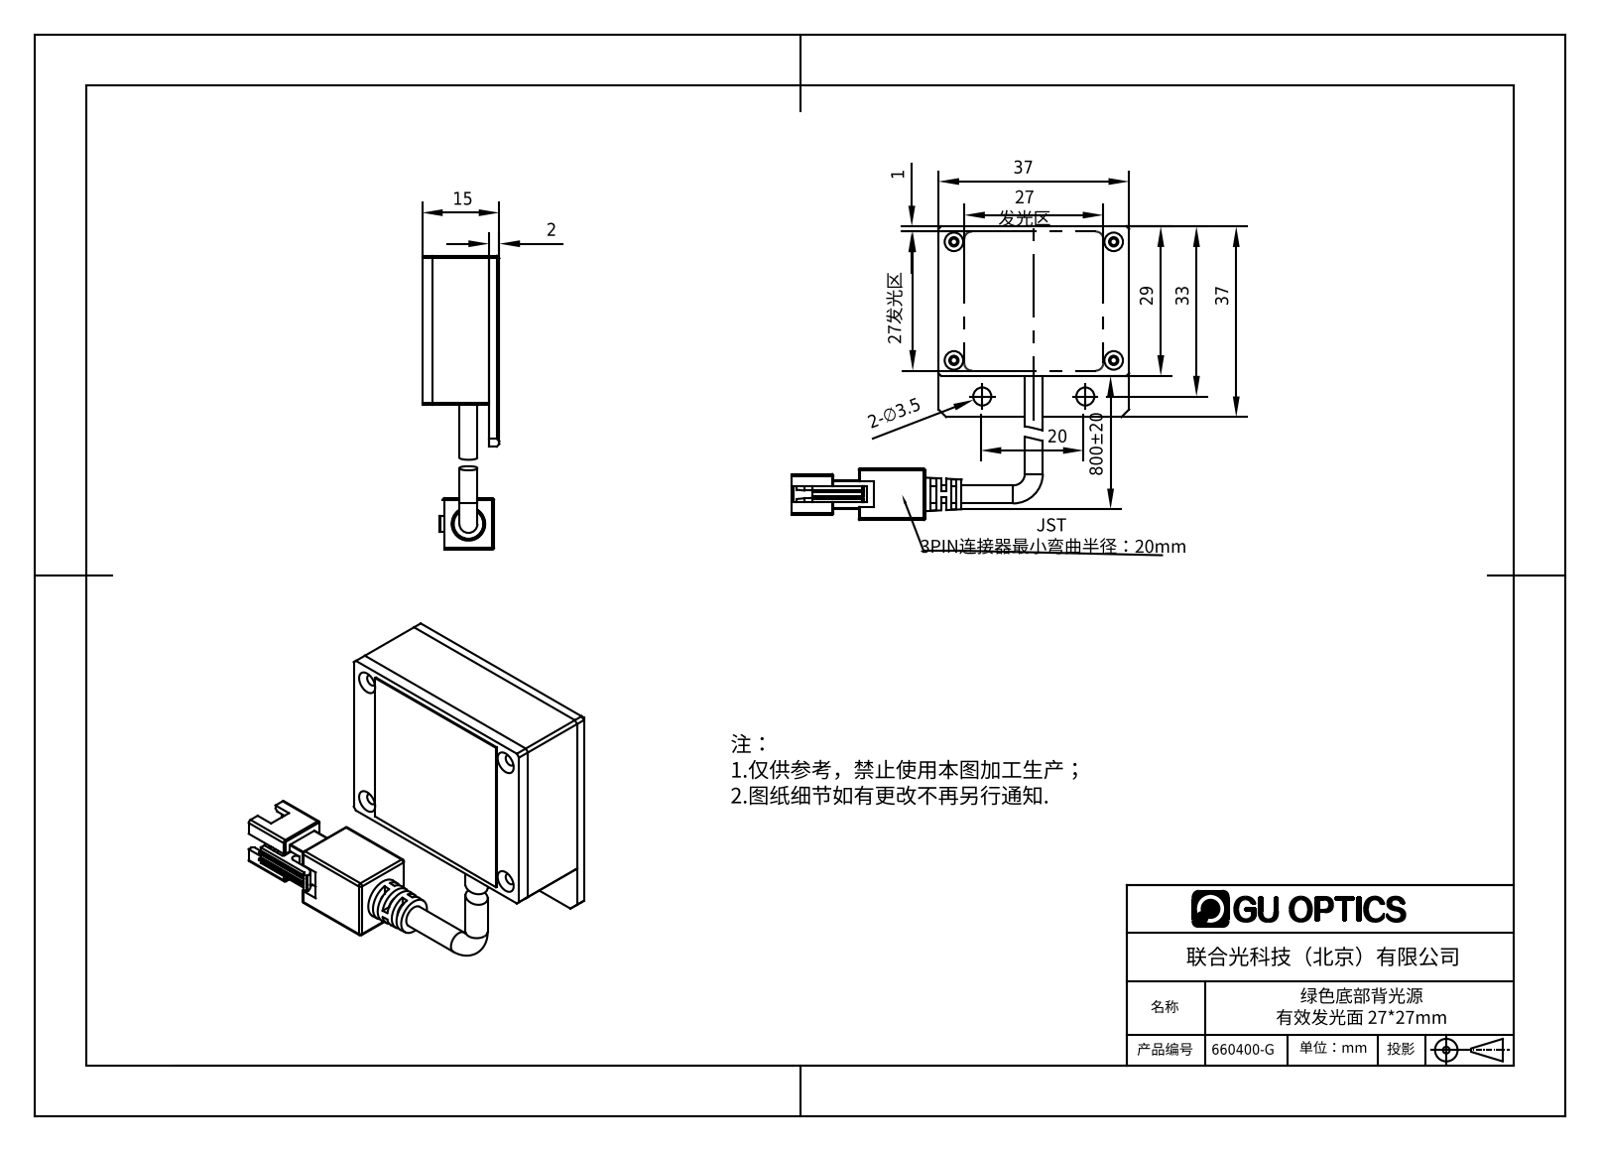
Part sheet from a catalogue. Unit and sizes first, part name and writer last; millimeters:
Units: millimetres
Overall size (bounding box): 65.5 × 57 × 15.2
Round holes (diameter × count): ⌀1.25 ×4, ⌀1.6 ×4, ⌀1.8 ×4, ⌀2 ×4, ⌀2.4 ×4, ⌀3.5 ×2
Round bosses / shafts (diameter × count): ⌀3.5 ×2
Partial cylindrical surfaces — rounded edges, fillets, slot ends (radius × count): R0.1 ×15, R0.2 ×13, R0.4 ×12, R1 ×4, R1.5 ×4, R0.75 ×2, R0.8 ×2, R0.3 ×1
Main face-to-face distances: 2, 1, 11, 13, 2.3, 10.7, 1.3, 28, 2.2, 15.2
Hole centre spacings: 8.9, 23, 26.44, 30.5, 31, 38.6, 39.37, 20
Volume: 11 682 mm³ · Surface area: 12 966 mm²
Bodies: 6 solids, 616 faces (375 planar, 122 cylindrical, 119 other)
Part name (STEP PRODUCT): 660400-G
STEP written by: SolidWorks 2016 (AUTOMOTIVE_DESIGN)
